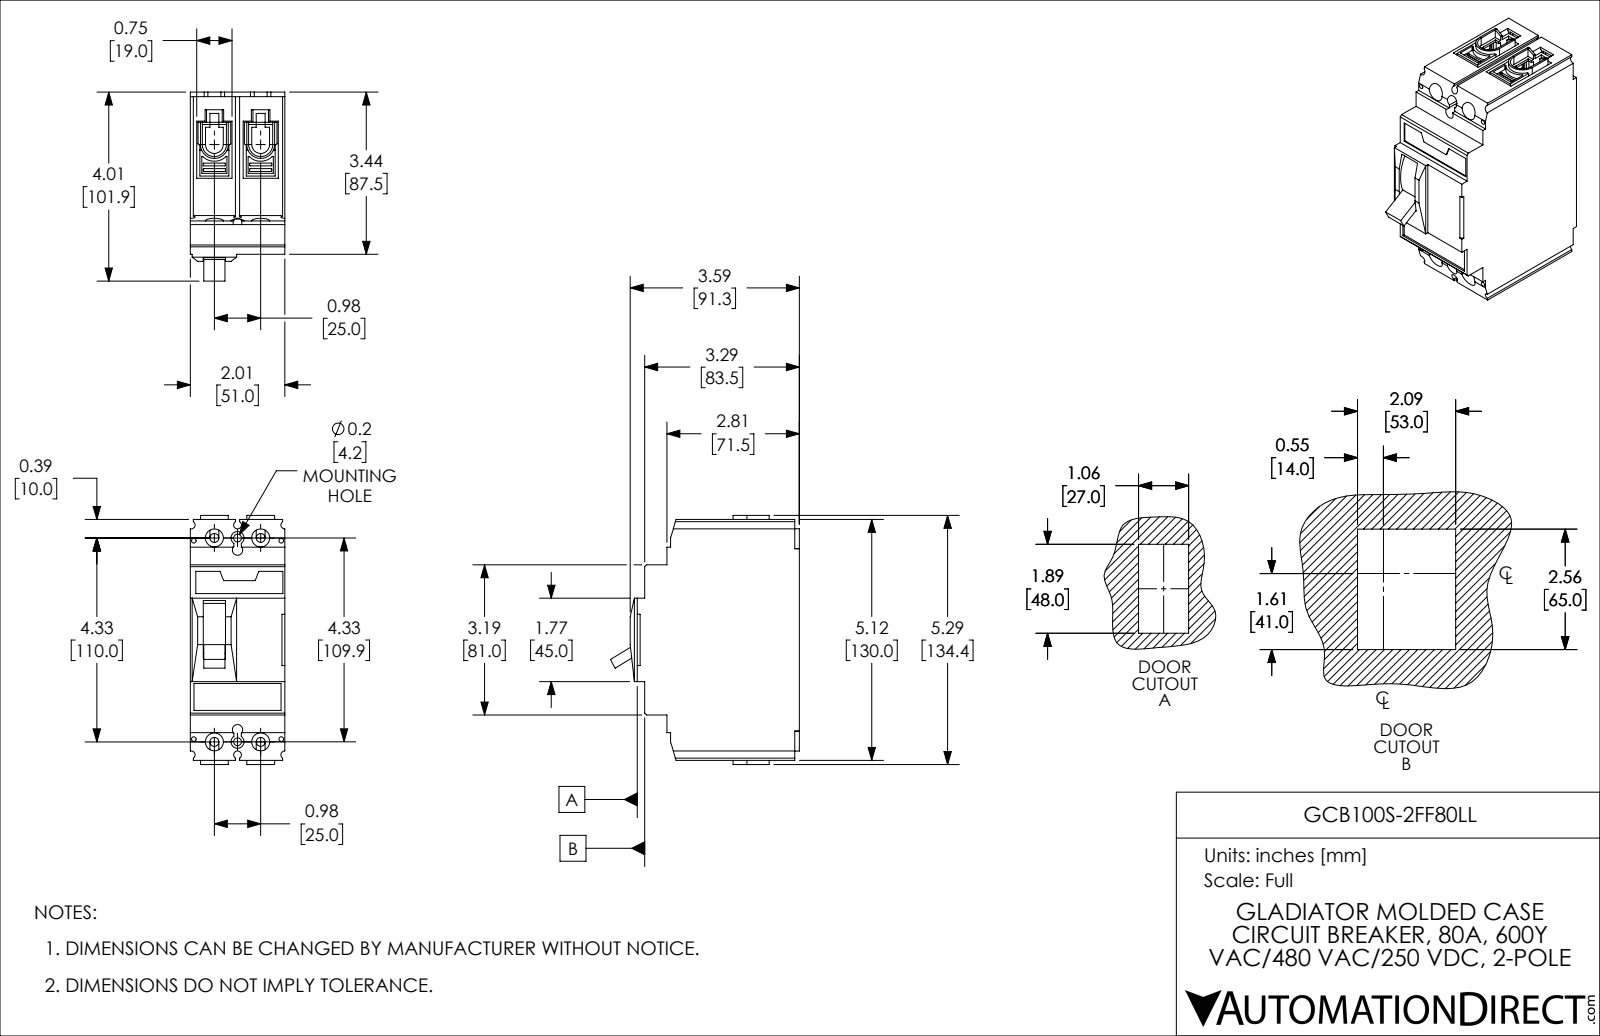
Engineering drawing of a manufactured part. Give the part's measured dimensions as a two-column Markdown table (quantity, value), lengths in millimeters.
| quantity | value |
| --- | --- |
| part name | GCB100S-2FF80LL |
| STEP written by | SolidWorks 2021 (CONFIG_CONTROL_DESIGN) |
| units | millimeters |
| bodies | 1 solid, 839 faces (529 planar, 278 cylindrical, 32 other) |
| overall size | 134.4 × 101.9 × 51 |
| volume | 476 900 mm³ |
| surface area | 71 230 mm² |
| round holes (diameter × count) | 2.5 × 4, 4.2 × 4, 4.8 × 4, 9.7 × 4, 7 × 2 |
| partial cylindrical surfaces (radius × count) | 0.3 × 58, 0.5 × 26, 1 × 10, 4 × 10, 0.6 × 4, 2.1 × 4, 2.8 × 2, 4.8 × 2 |
| main face-to-face distances | 51, 25, 15.8, 114.2, 19, 47.5, 2.8, 22.5, 28.5, 3.5 |
| hole center spacings | 11.2, 12.5, 14.3, 23.6, 25.1, 36.1, 109.1, 110.7 |
